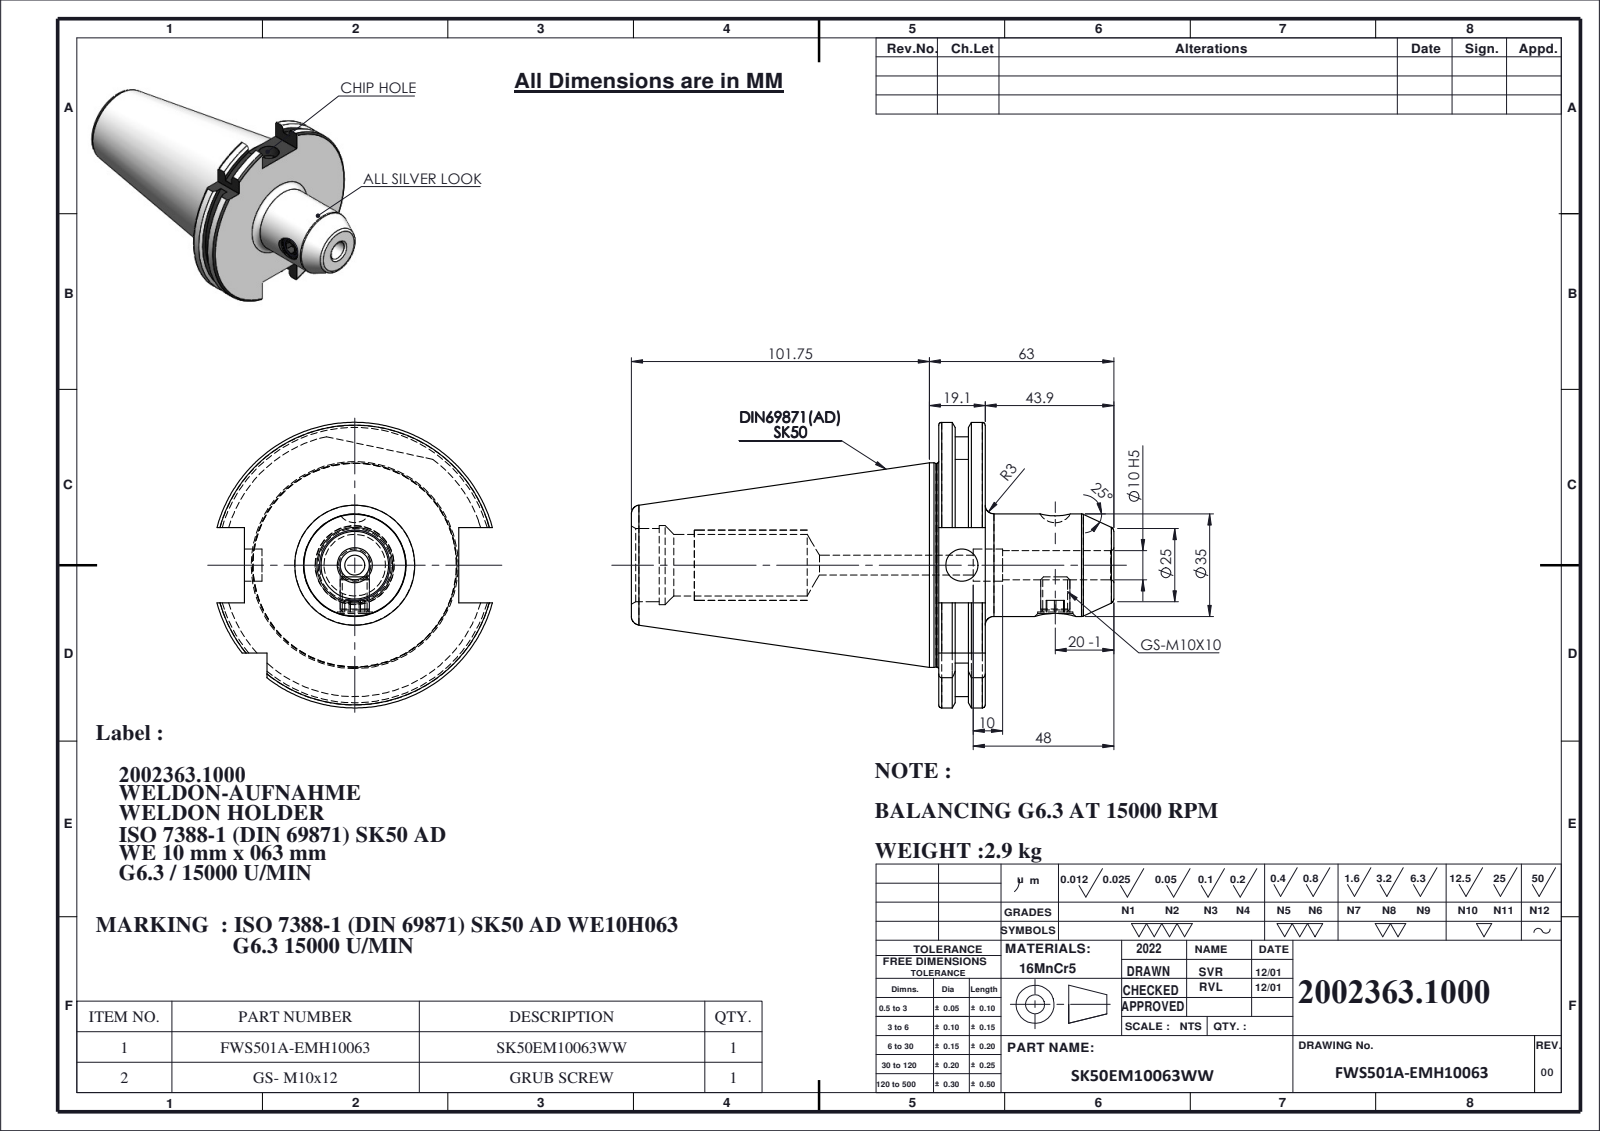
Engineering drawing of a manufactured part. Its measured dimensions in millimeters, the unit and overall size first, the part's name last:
Units: millimetres
Overall size (bounding box): 164.75 × 97.5 × 94.05
Round holes (diameter × count): ⌀11 ×2, ⌀6.8 ×1, ⌀8.5 ×1, ⌀10 ×1, ⌀12 ×1, ⌀21 ×1, ⌀25 ×1, ⌀27 ×1
Round bosses / shafts (diameter × count): ⌀69.85 ×1, ⌀69.45 ×1, ⌀35 ×1, ⌀10 ×1
Partial cylindrical surfaces — rounded edges, fillets, slot ends (radius × count): R44.9 ×1, R48.75 ×1
Main face-to-face distances: 15.9, 5.66, 10.24, 10.15, 4.49, 5.75, 104.95, 110.61, 115.1, 120.85
Volume: 372 919 mm³ · Surface area: 48 212 mm²
Bodies: 2 solids, 125 faces (33 planar, 39 cylindrical, 53 other)
Part name (STEP PRODUCT): SK50EM10063WW; 91506-WE110063; GS-M10X12-DIN1835-B
STEP written by: SolidWorks 2018 (CONFIG_CONTROL_DESIGN)
